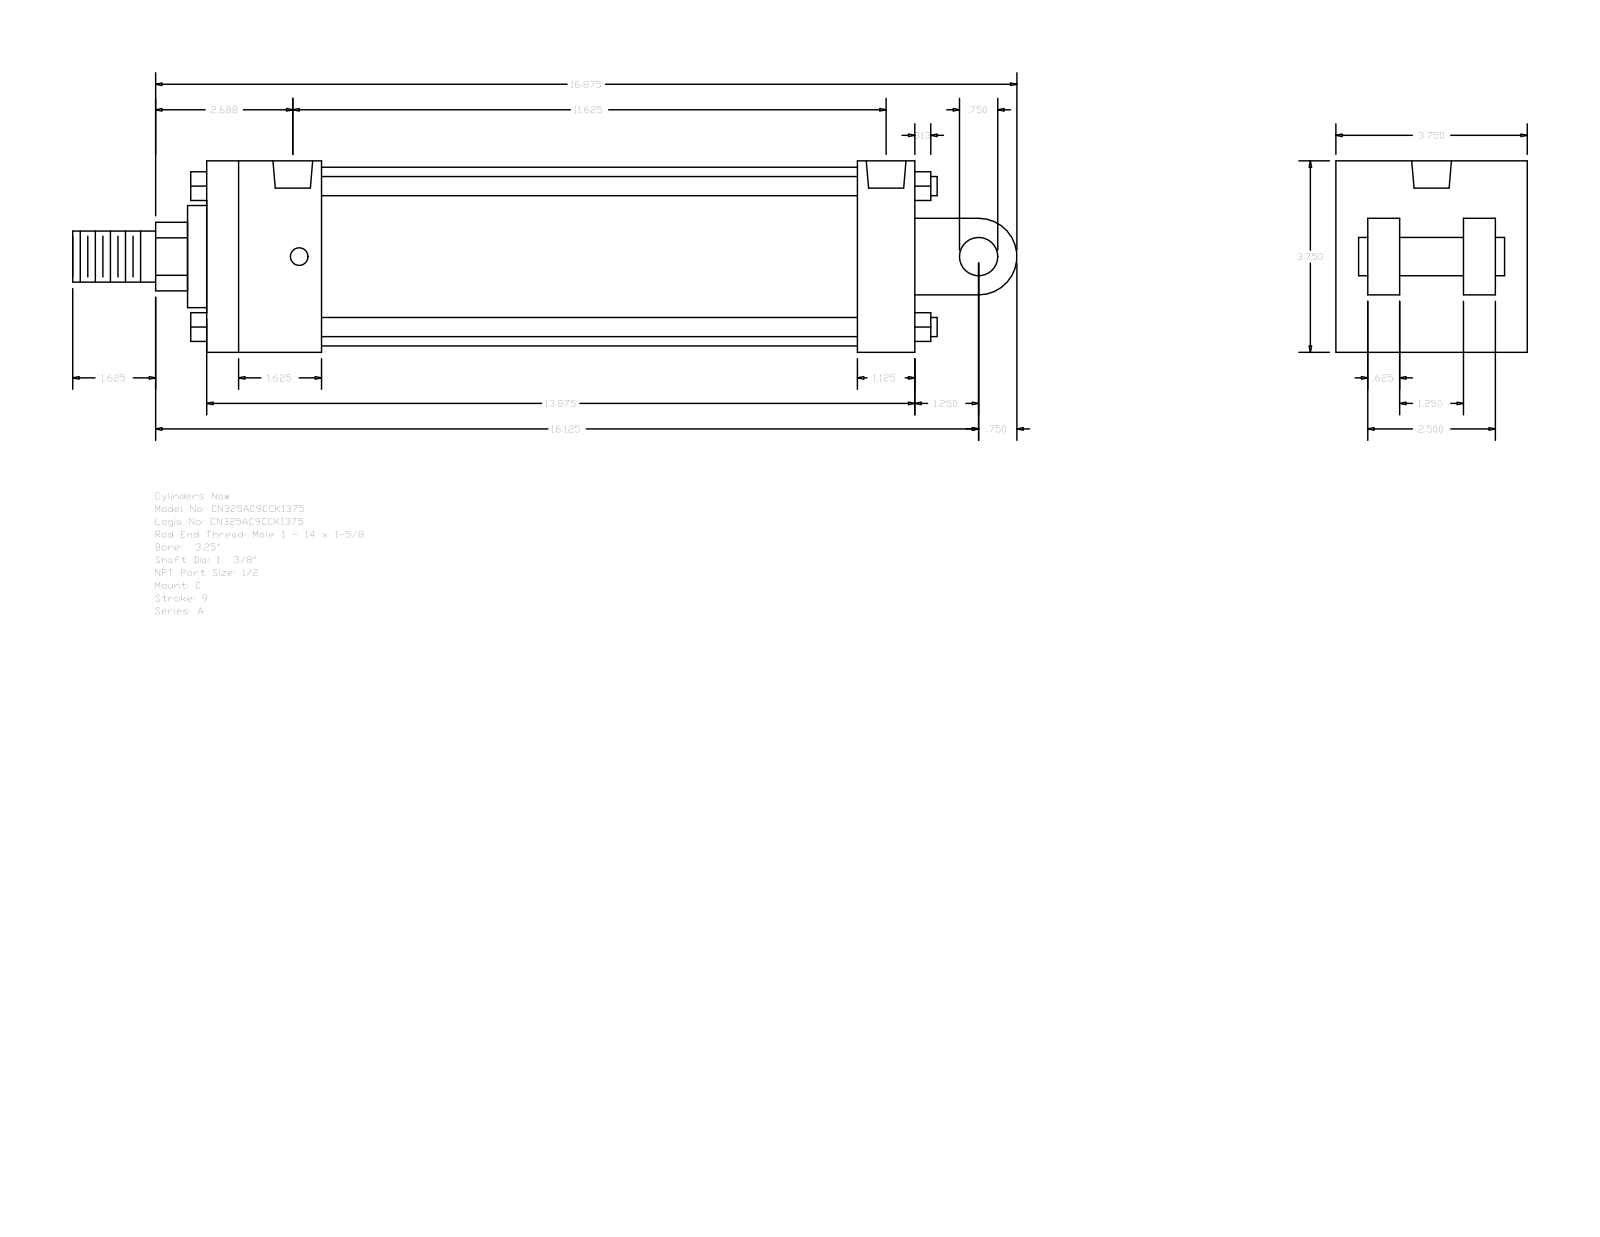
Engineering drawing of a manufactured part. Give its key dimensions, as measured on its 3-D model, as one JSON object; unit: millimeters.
{"part_name": "A_C__0325_1.375", "step_written_by": "GSSL Pune (CONFIG_CONTROL_DESIGN)", "units": "millimeters", "bodies": {"solids": 0, "faces": 135, "planar": 102, "cylindrical": 33, "other": 0}, "overall_size": [469.9, 95.25, 95.25], "round_holes": [[8.73, 4], [19.77, 2]], "round_bosses_or_shafts": [[9.53, 4], [88.9, 1], [50.8, 1], [34.92, 1], [25.4, 1], [19.05, 1]], "partial_cylinders_radius": [[17.06, 1], [19.05, 1]], "face_to_face_distances": [95.24, 352.42, 15.87, 28.57, 63.5, 66.67, 57.15, 79.37, 31.74, 47.63], "hole_center_spacings": [3.18, 288.92, 292.1, 295.28]}
